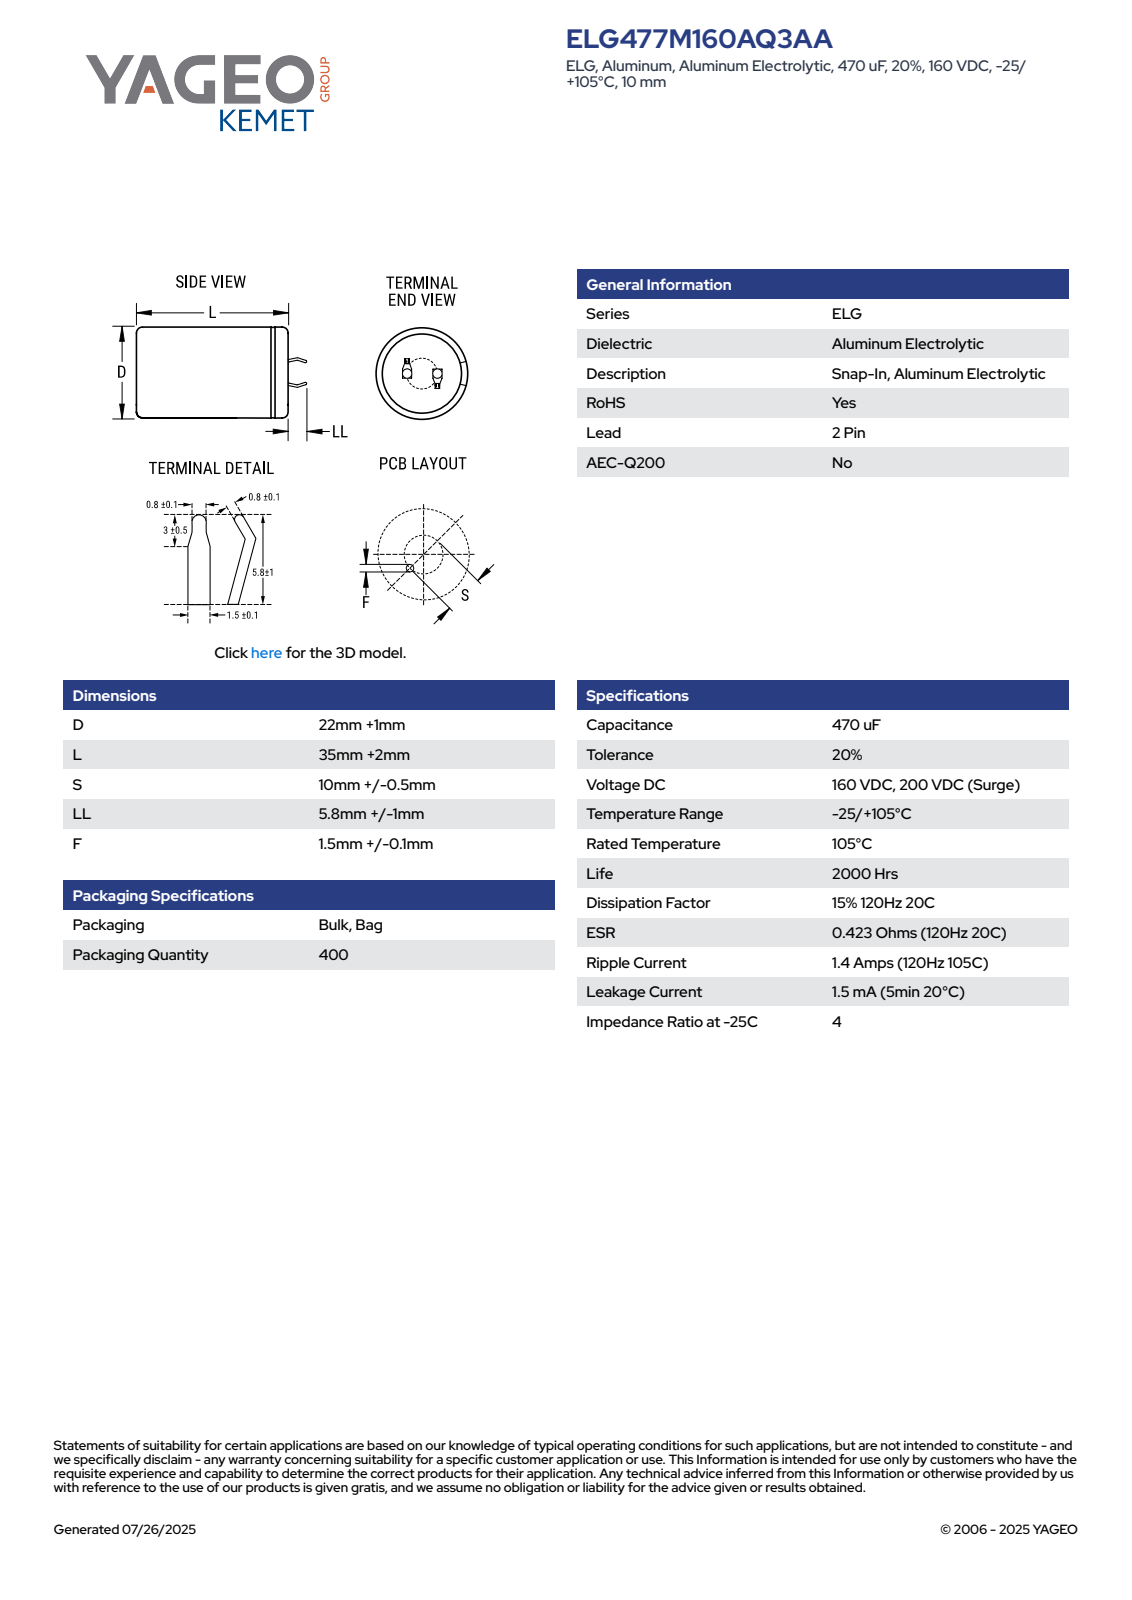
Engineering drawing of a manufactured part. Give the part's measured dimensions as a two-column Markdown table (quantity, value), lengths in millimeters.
| quantity | value |
| --- | --- |
| part name | CARS_K2P_22X35_D23L37S10LL6.8F1.6 |
| STEP written by | SolidWorks 2014 (AUTOMOTIVE_DESIGN) |
| units | millimeters |
| bodies | 1 solid, 100 faces (52 planar, 9 cylindrical, 39 other) |
| overall size | 43.79 × 23 × 23 |
| volume | 15 243 mm³ |
| surface area | 3 529 mm² |
| round holes (diameter × count) | 20.35 × 1 |
| round bosses / shafts (diameter × count) | 23 × 1 |
| partial cylindrical surfaces (radius × count) | 11.49 × 1 |
| main face-to-face distances | 36.99, 37.49, 0.5, 0.6, 7.08, 0.75, 1.35, 7.68, 6.48, 0.59 |
